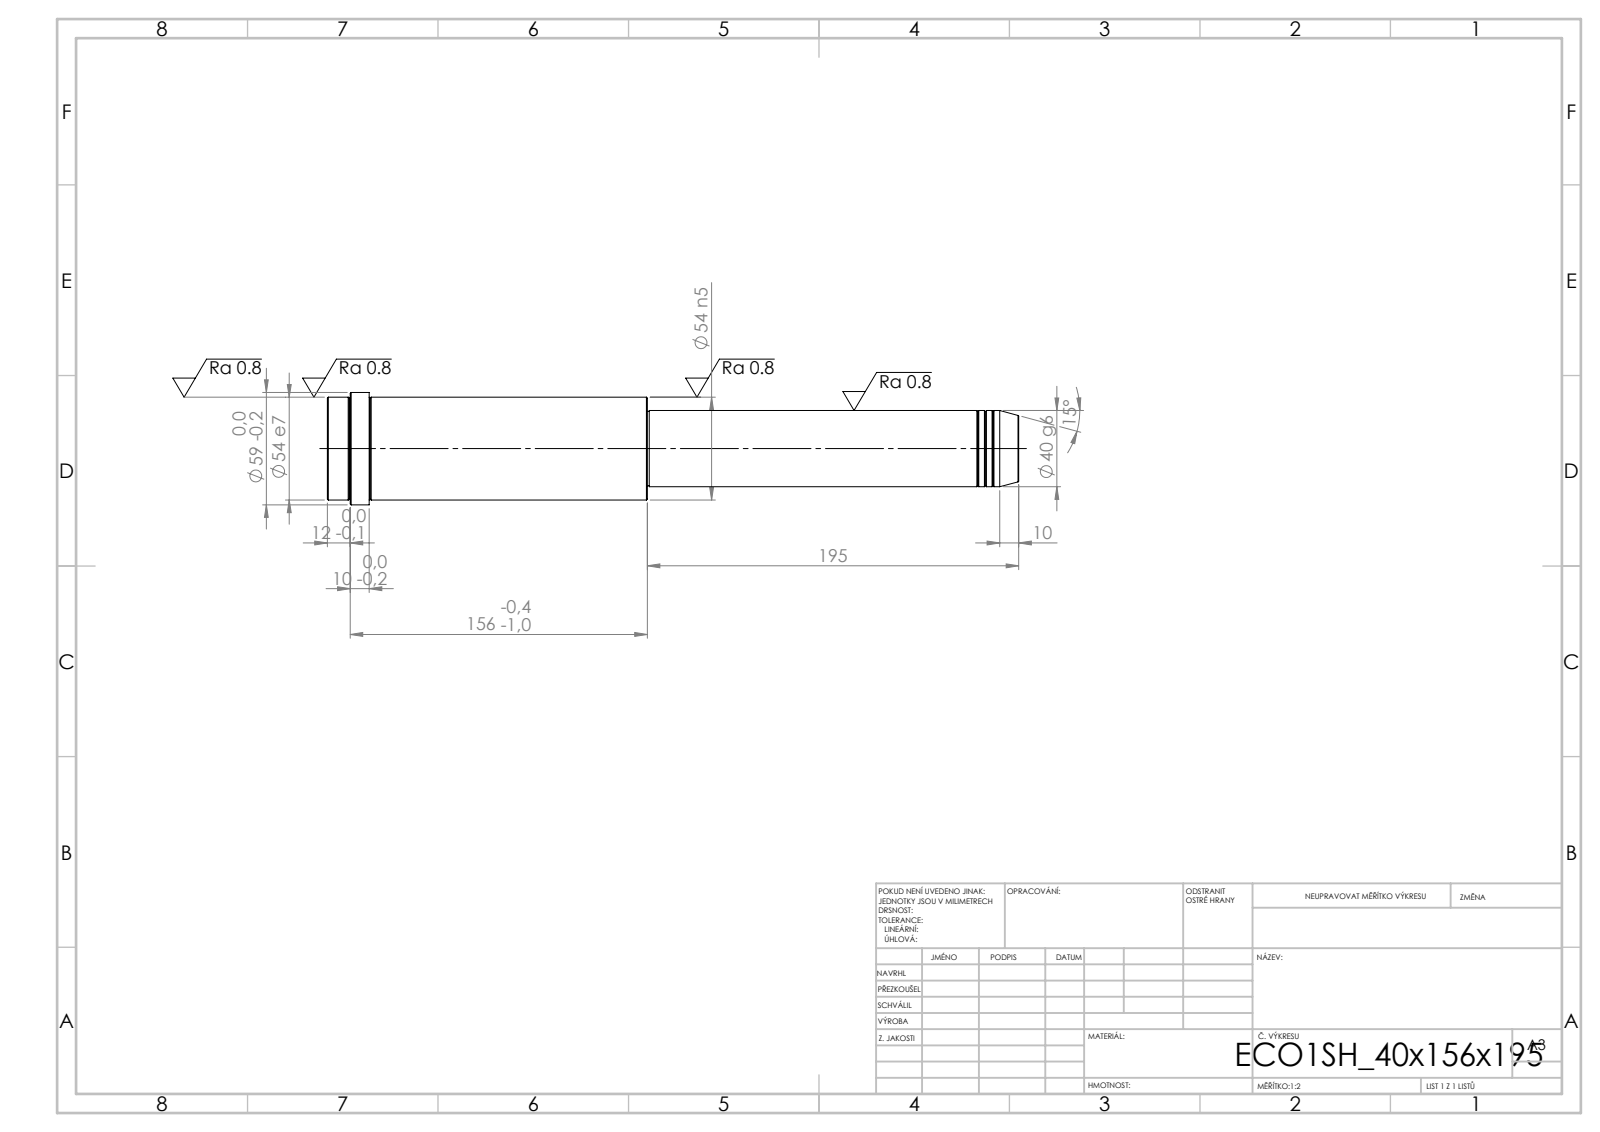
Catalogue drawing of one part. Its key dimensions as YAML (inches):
step_written_by: "SolidWorks 2019 (CONFIG_CONTROL_DESIGN)"
units: inches
bodies: {solids: 1, faces: 52, planar: 6, cylindrical: 16, other: 30}
overall_size: [14.291, 2.323, 2.323]
volume: 38.58
surface_area: 90.86
round_bosses_or_shafts:
  - {diameter: 2.323, count: 1}
  - {diameter: 2.126, count: 1}
  - {diameter: 1.575, count: 1}
  - {diameter: 1.535, count: 1}
face_to_face_distances: [6.614, 7.677, 14.291, 13.425, 5.748, 0.866, 13.819, 6.142, 0.394, 0.472]
